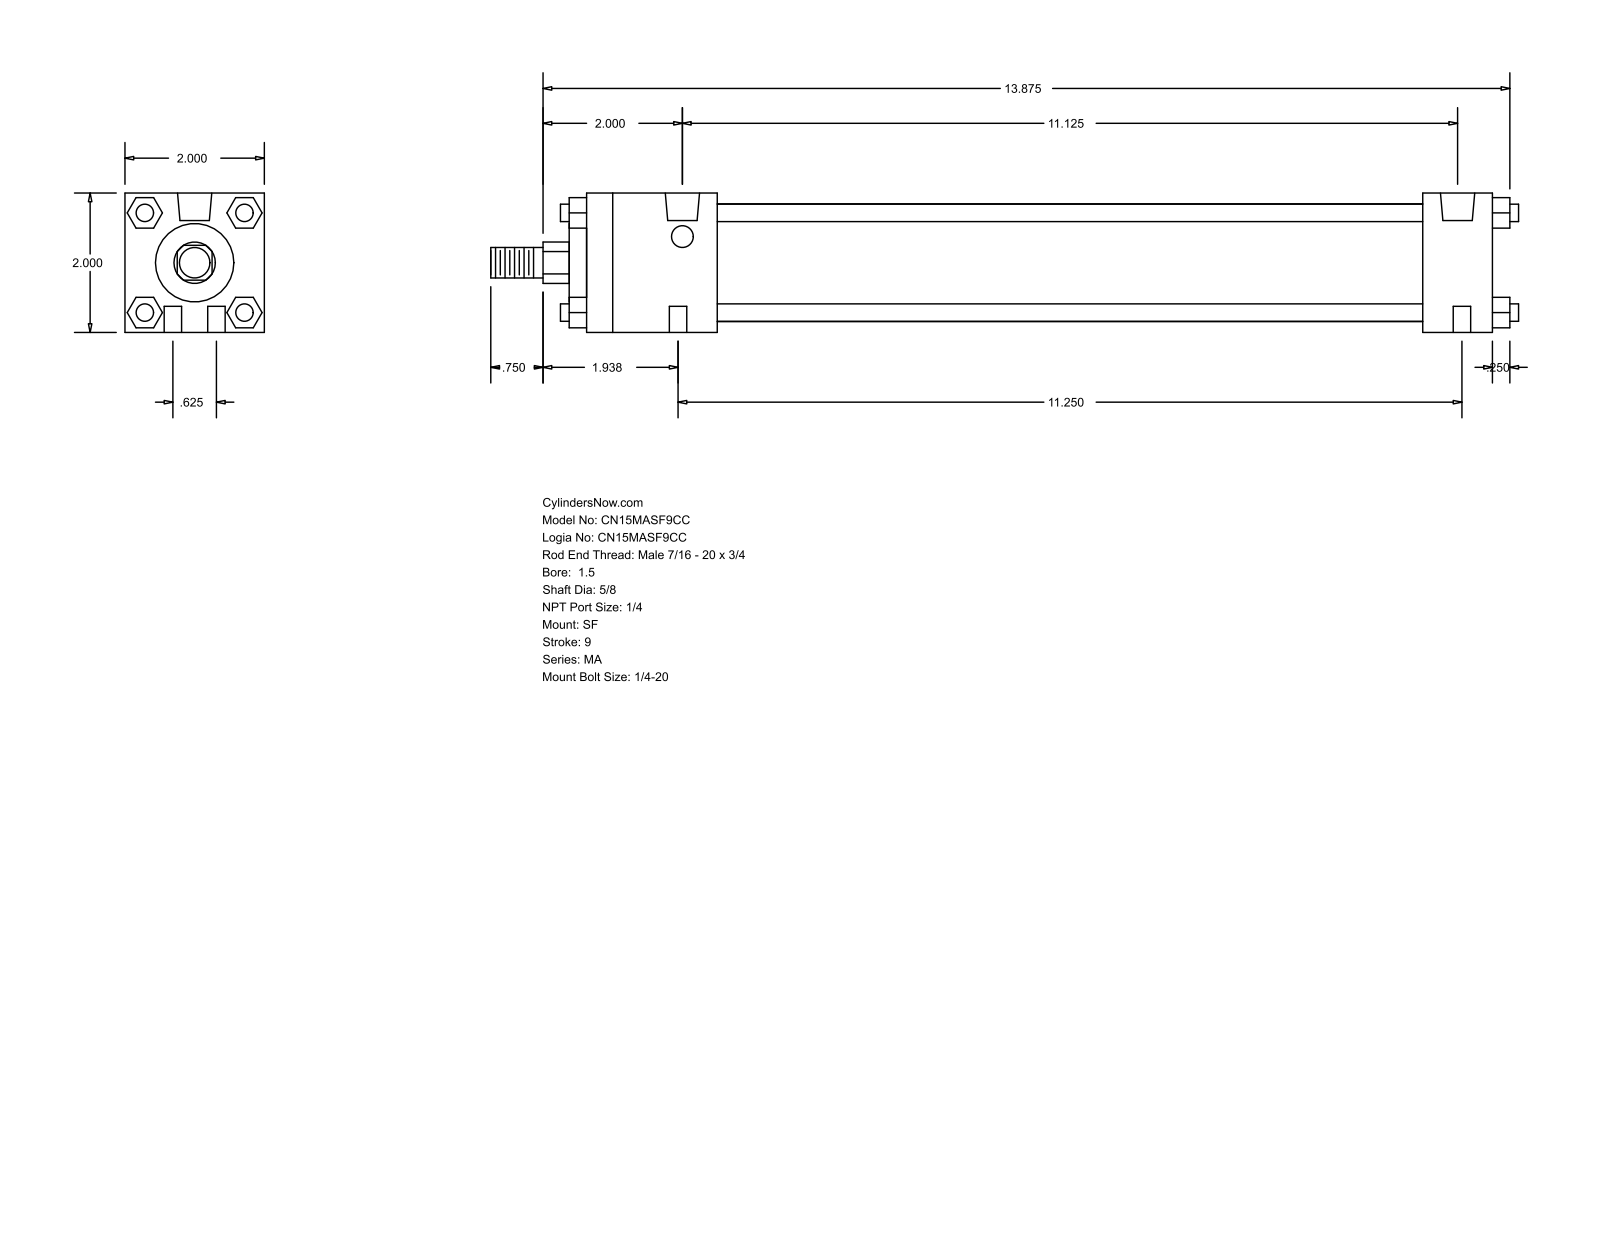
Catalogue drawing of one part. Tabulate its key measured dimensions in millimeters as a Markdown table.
| quantity | value |
| --- | --- |
| part name | MA_SF__0150_0.625 |
| STEP written by | GSSL Pune (CONFIG_CONTROL_DESIGN) |
| units | millimeters |
| bodies | 0 solids, 124 faces (94 planar, 30 cylindrical, 0 other) |
| overall size | 374.65 × 50.8 × 50.8 |
| round holes (diameter × count) | 6.35 × 4, 7.94 × 2, 12.49 × 2 |
| round bosses / shafts (diameter × count) | 6.35 × 4, 42.93 × 1, 28.57 × 1, 15.88 × 1, 11.11 × 1 |
| partial cylindrical surfaces (radius × count) | 7.54 × 1 |
| main face-to-face distances | 50.8, 330.19, 47.62, 304.8, 257.18, 282.57, 25.39, 6.35, 53.97, 311.15 |
| hole center spacings | 8.1, 15.88, 282.58, 284.27, 284.28, 285.75, 286.19 |
